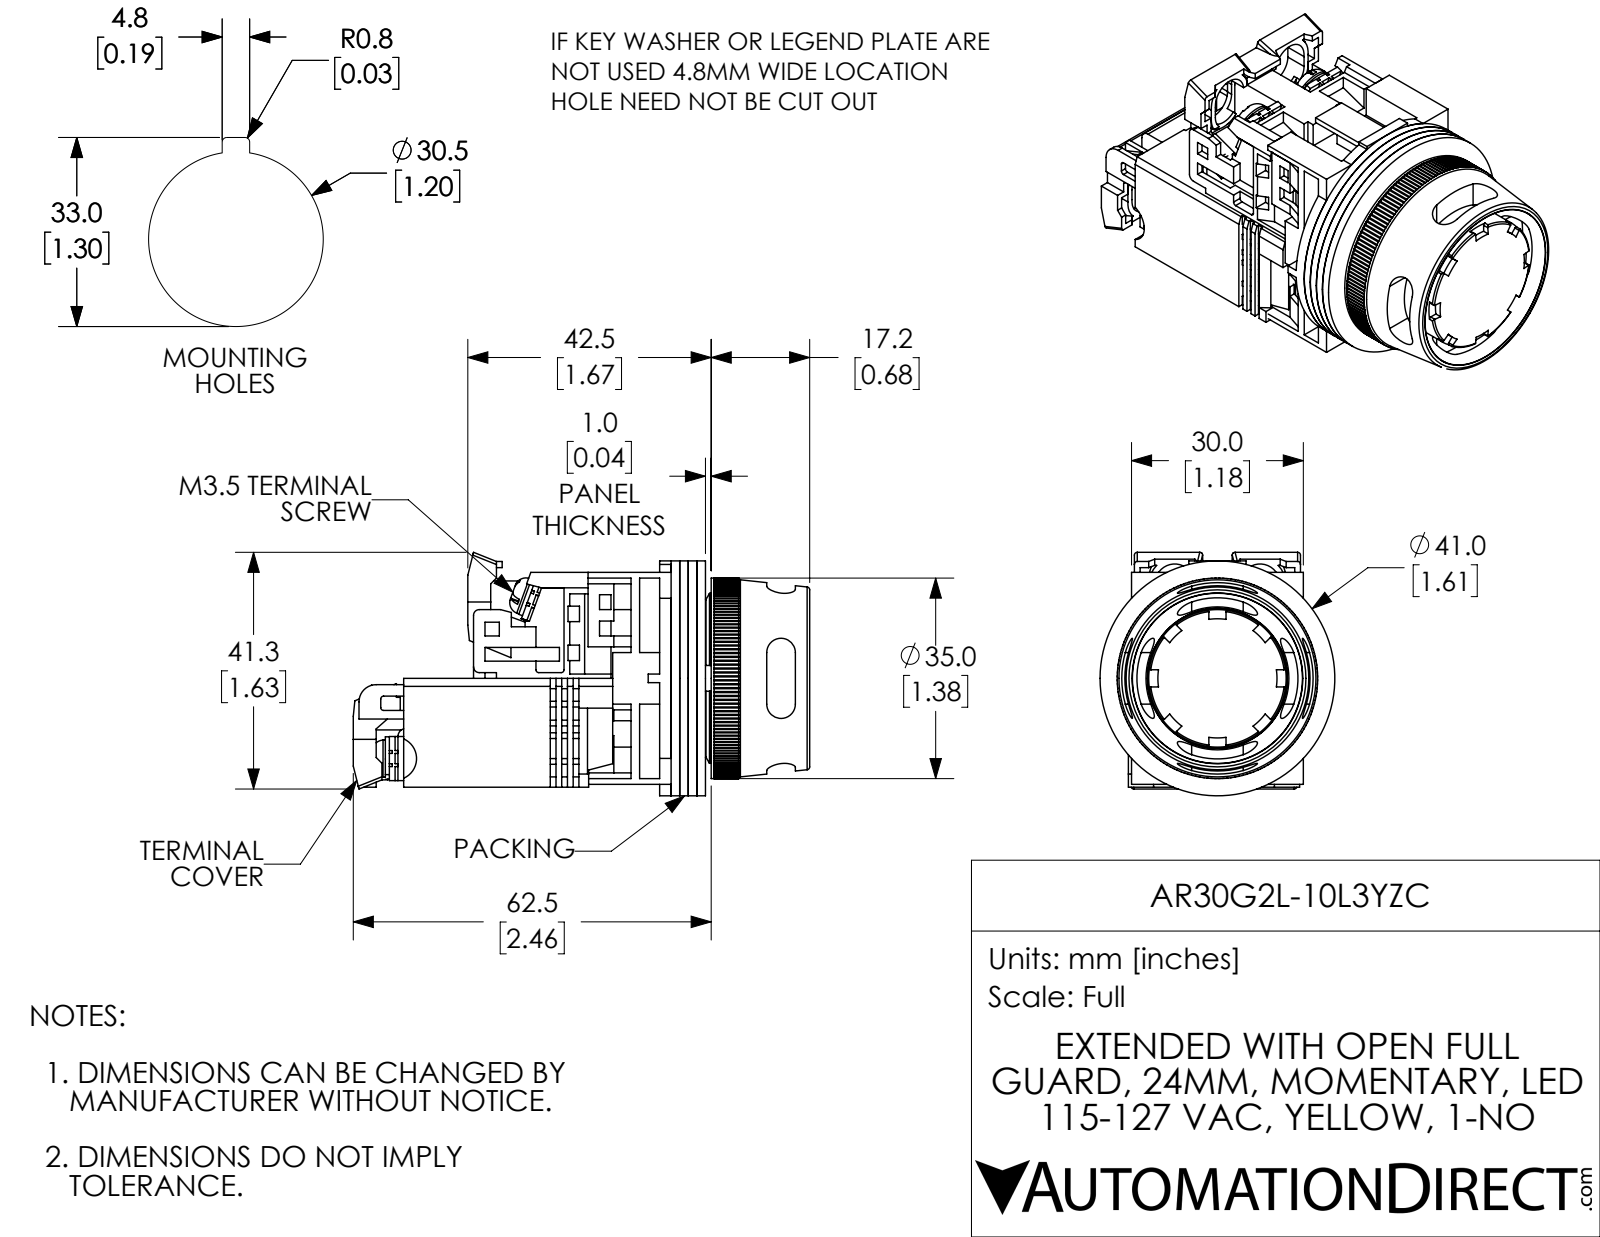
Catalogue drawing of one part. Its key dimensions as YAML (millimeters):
part_name: "AR30G2L-10L3YZC"
step_written_by: "SolidWorks 2017 (AUTOMOTIVE_DESIGN)"
units: millimeters
bodies: {solids: 27, faces: 2102, planar: 1483, cylindrical: 474, other: 145}
overall_size: [79.7, 42.5, 41]
volume: 47620
surface_area: 43030
round_holes:
  - {diameter: 3.5, count: 6}
  - {diameter: 3.6, count: 4}
  - {diameter: 3, count: 3}
  - {diameter: 12, count: 1}
  - {diameter: 18, count: 1}
  - {diameter: 18.5, count: 1}
  - {diameter: 20, count: 1}
  - {diameter: 24, count: 1}
  - {diameter: 31.8, count: 1}
round_bosses_or_shafts:
  - {diameter: 6.6, count: 4}
  - {diameter: 3.5, count: 2}
  - {diameter: 41, count: 1}
  - {diameter: 35, count: 1}
  - {diameter: 30, count: 1}
  - {diameter: 22, count: 1}
  - {diameter: 19.7, count: 1}
  - {diameter: 14, count: 1}
partial_cylinders:
  - {radius: 0.3, count: 160}
  - {radius: 1.5, count: 17}
  - {radius: 0.3, count: 16}
  - {radius: 0.5, count: 13}
  - {radius: 2.5, count: 4}
  - {radius: 3.5, count: 4}
  - {radius: 4.5, count: 4}
  - {radius: 1, count: 2}
face_to_face_distances: [1.5, 3, 4.5, 1, 19, 7, 2, 36, 17.5, 3.5]
hole_center_spacings: [14.7, 0.5, 7, 8.1, 8.3, 14.8, 14.8, 15.5]
